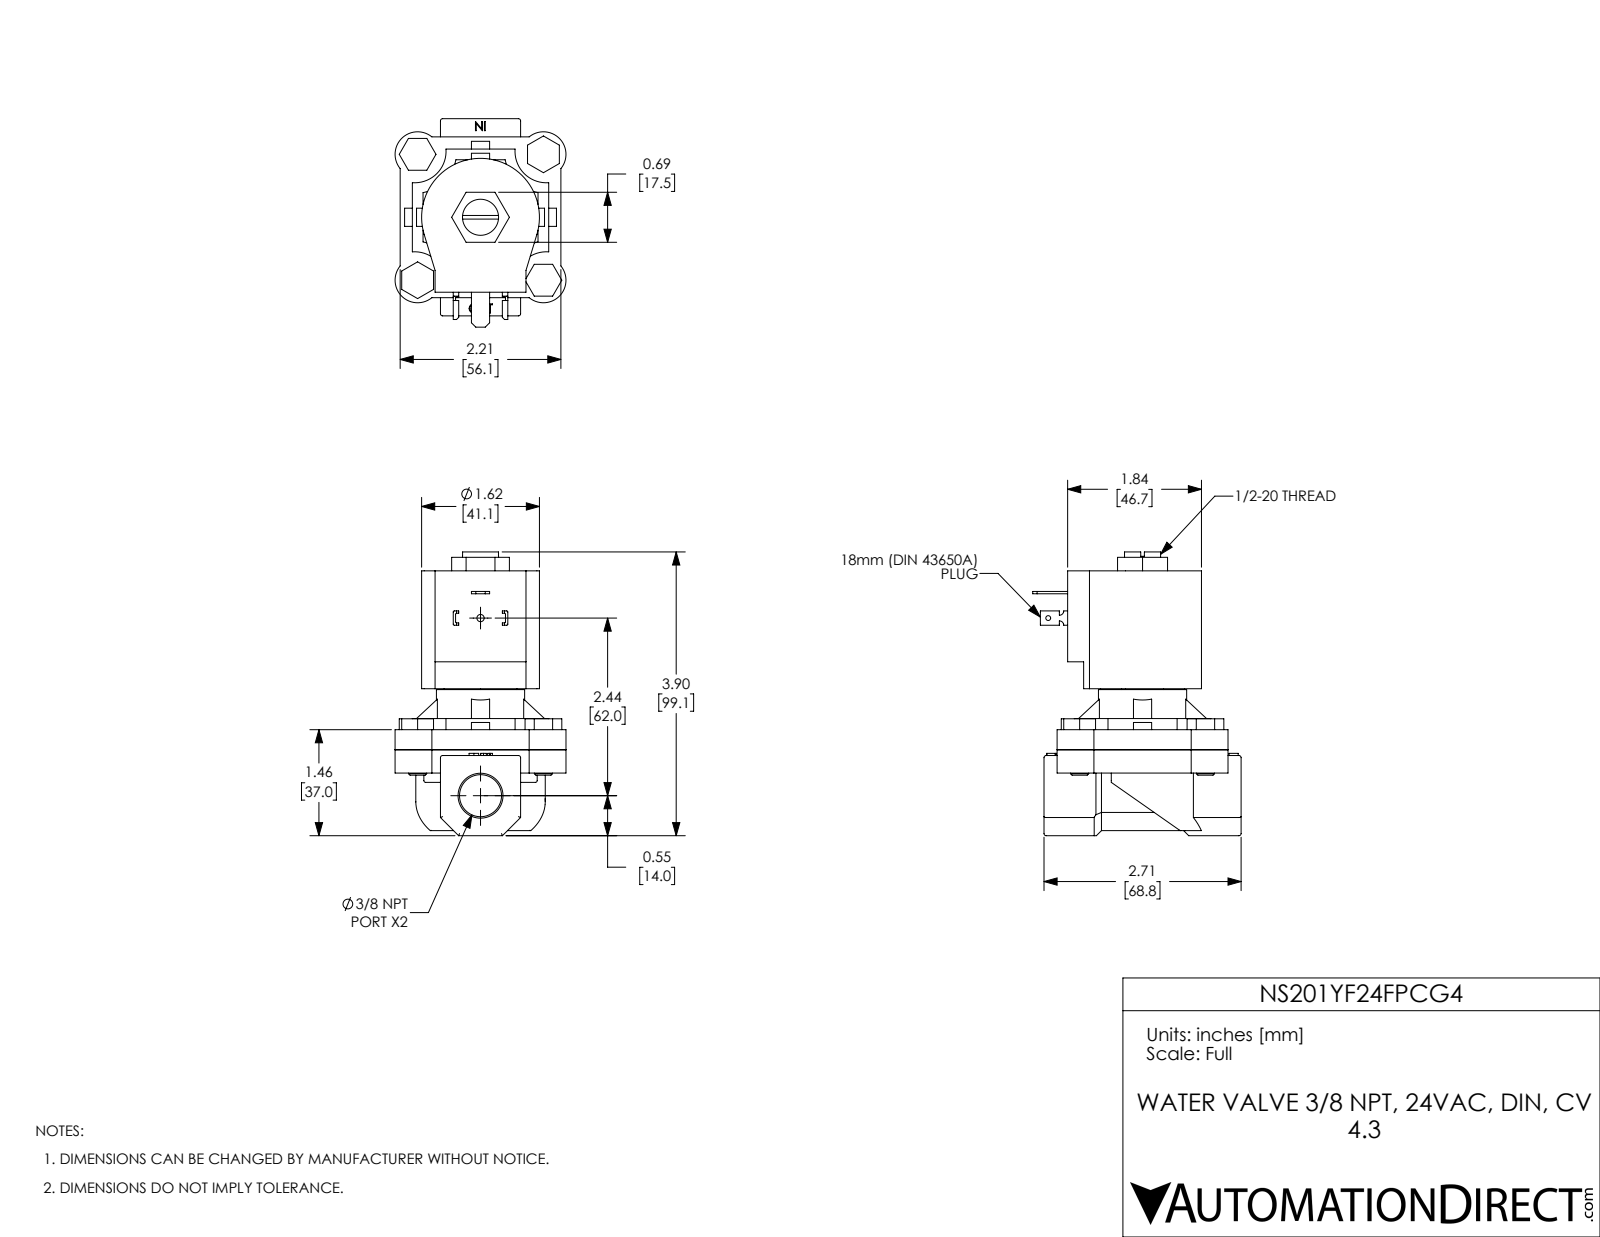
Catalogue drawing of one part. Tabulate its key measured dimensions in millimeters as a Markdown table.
| quantity | value |
| --- | --- |
| part name | NS201YF24FPCG4 |
| STEP written by | SolidWorks 2017 (AUTOMOTIVE_DESIGN) |
| units | millimeters |
| bodies | 11 solids, 383 faces (237 planar, 113 cylindrical, 33 other) |
| overall size | 99.1 × 72.8 × 59.7 |
| volume | 168 300 mm³ |
| surface area | 42 940 mm² |
| round holes (diameter × count) | 6.4 × 4, 1.7 × 1, 2.5 × 1, 12.6 × 1, 13 × 1, 14.7 × 1, 29.3 × 1 |
| round bosses / shafts (diameter × count) | 6.3 × 4, 30.8 × 1 |
| partial cylindrical surfaces (radius × count) | 0.8 × 15, 0.4 × 8, 7.9 × 4, 11 × 4, 14.7 × 4, 1.5 × 2, 20.6 × 1, 22.6 × 1 |
| main face-to-face distances | 7, 62.5, 55.4, 8.1, 15.1, 70.6, 14.1, 42.1, 6.4, 28 |
| hole center spacings | 31.1, 43.9, 62.1, 62 |
